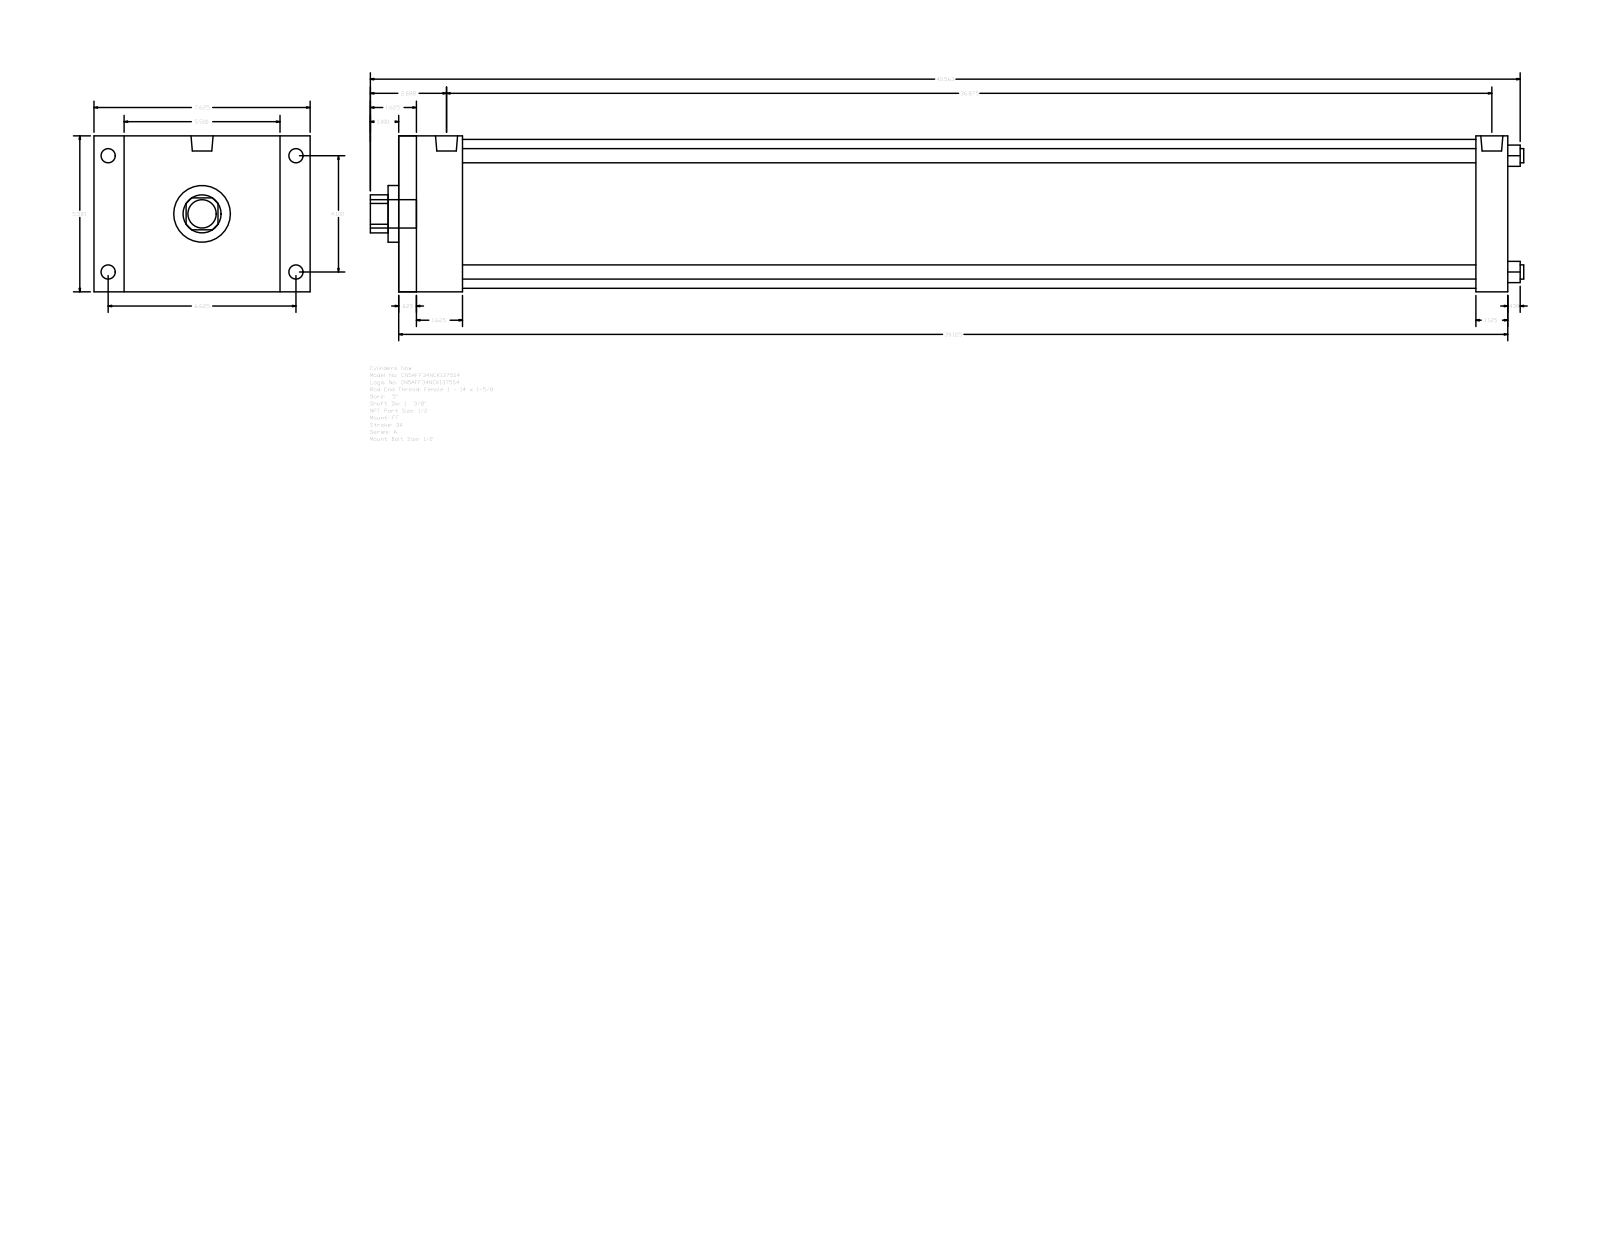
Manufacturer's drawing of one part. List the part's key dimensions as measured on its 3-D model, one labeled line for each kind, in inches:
Part name (STEP PRODUCT): A_FF__0500_1.375
STEP written by: GSSL Pune (CONFIG_CONTROL_DESIGN)
Units: inches
Bodies: 0 solids, 92 faces (64 planar, 28 cylindrical, 0 other)
Overall size (bounding box): 40.687 × 7.625 × 5.5
Round holes (diameter × count): ⌀0.5 ×4, ⌀1.375 ×1, ⌀2 ×1, ⌀5.25 ×1
Round bosses / shafts (diameter × count): ⌀0.5 ×4, ⌀0.344 ×4, ⌀0.778 ×2, ⌀1 ×1
Partial cylindrical surfaces — rounded edges, fillets, slot ends (radius × count): R0.672 ×1
Main face-to-face distances: 5.5, 39.125, 38.5, 0.625, 1.125, 38, 37.375, 2.25, 1.625, 35.75
Hole centre spacings: 2.899, 4.1, 5.798
